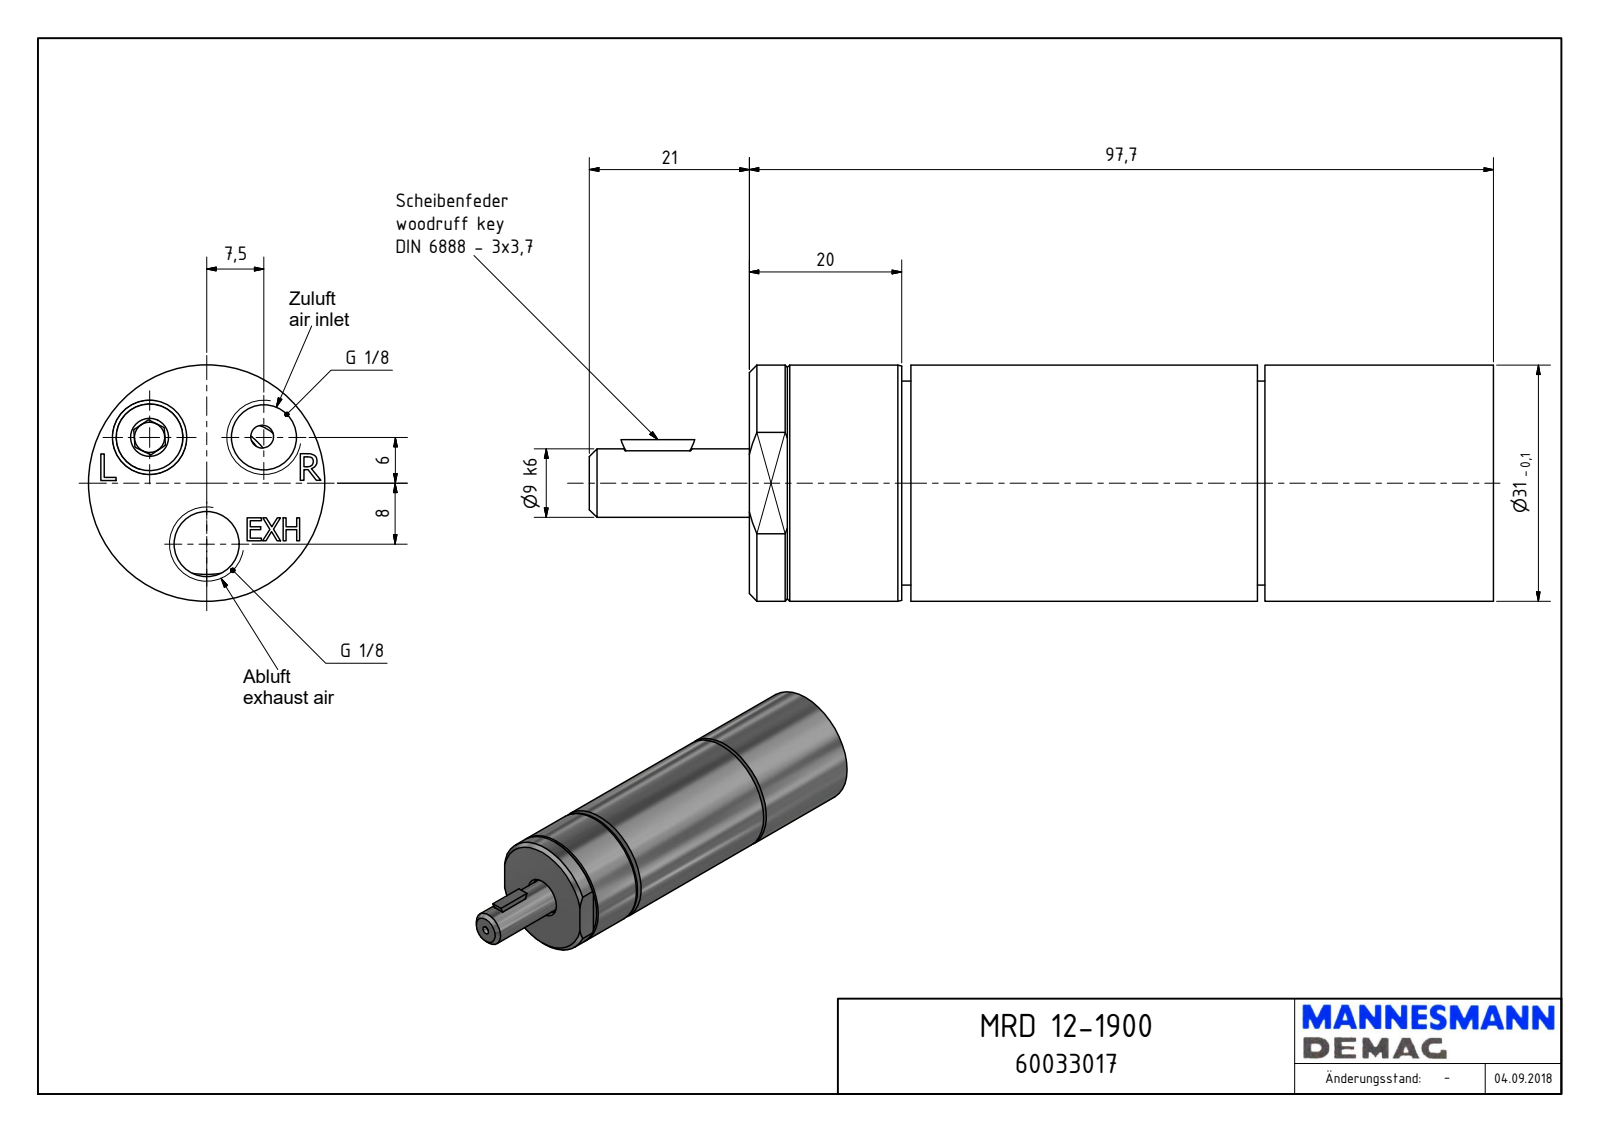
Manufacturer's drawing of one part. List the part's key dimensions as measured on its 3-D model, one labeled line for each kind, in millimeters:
Part name (STEP PRODUCT): MRD 12-1900_60033017
STEP written by: Autodesk Inventor 2018 (AUTOMOTIVE_DESIGN)
Units: millimetres
Bodies: 1 solid, 161 faces (105 planar, 31 cylindrical, 25 other)
Overall size (bounding box): 118.7 × 31 × 31
Volume: 72 555 mm³ · Surface area: 14 236 mm²
Round holes (diameter × count): ⌀8.57 ×3, ⌀1 ×1, ⌀4 ×1, ⌀10.5 ×1, ⌀29.3 ×1
Round bosses / shafts (diameter × count): ⌀31 ×1, ⌀28 ×1, ⌀26.78 ×1, ⌀9 ×1
Partial cylindrical surfaces — rounded edges, fillets, slot ends (radius × count): R1.5 ×2, R4 ×2, R5 ×1, R5.25 ×1, R10.96 ×1, R12 ×1, R14.25 ×1
Main face-to-face distances: 97.7, 66.7, 31, 21.2, 45.5, 76.5, 67.7, 46.5, 1, 30
Hole centre spacings: 9.6, 15.88, 8, 15
